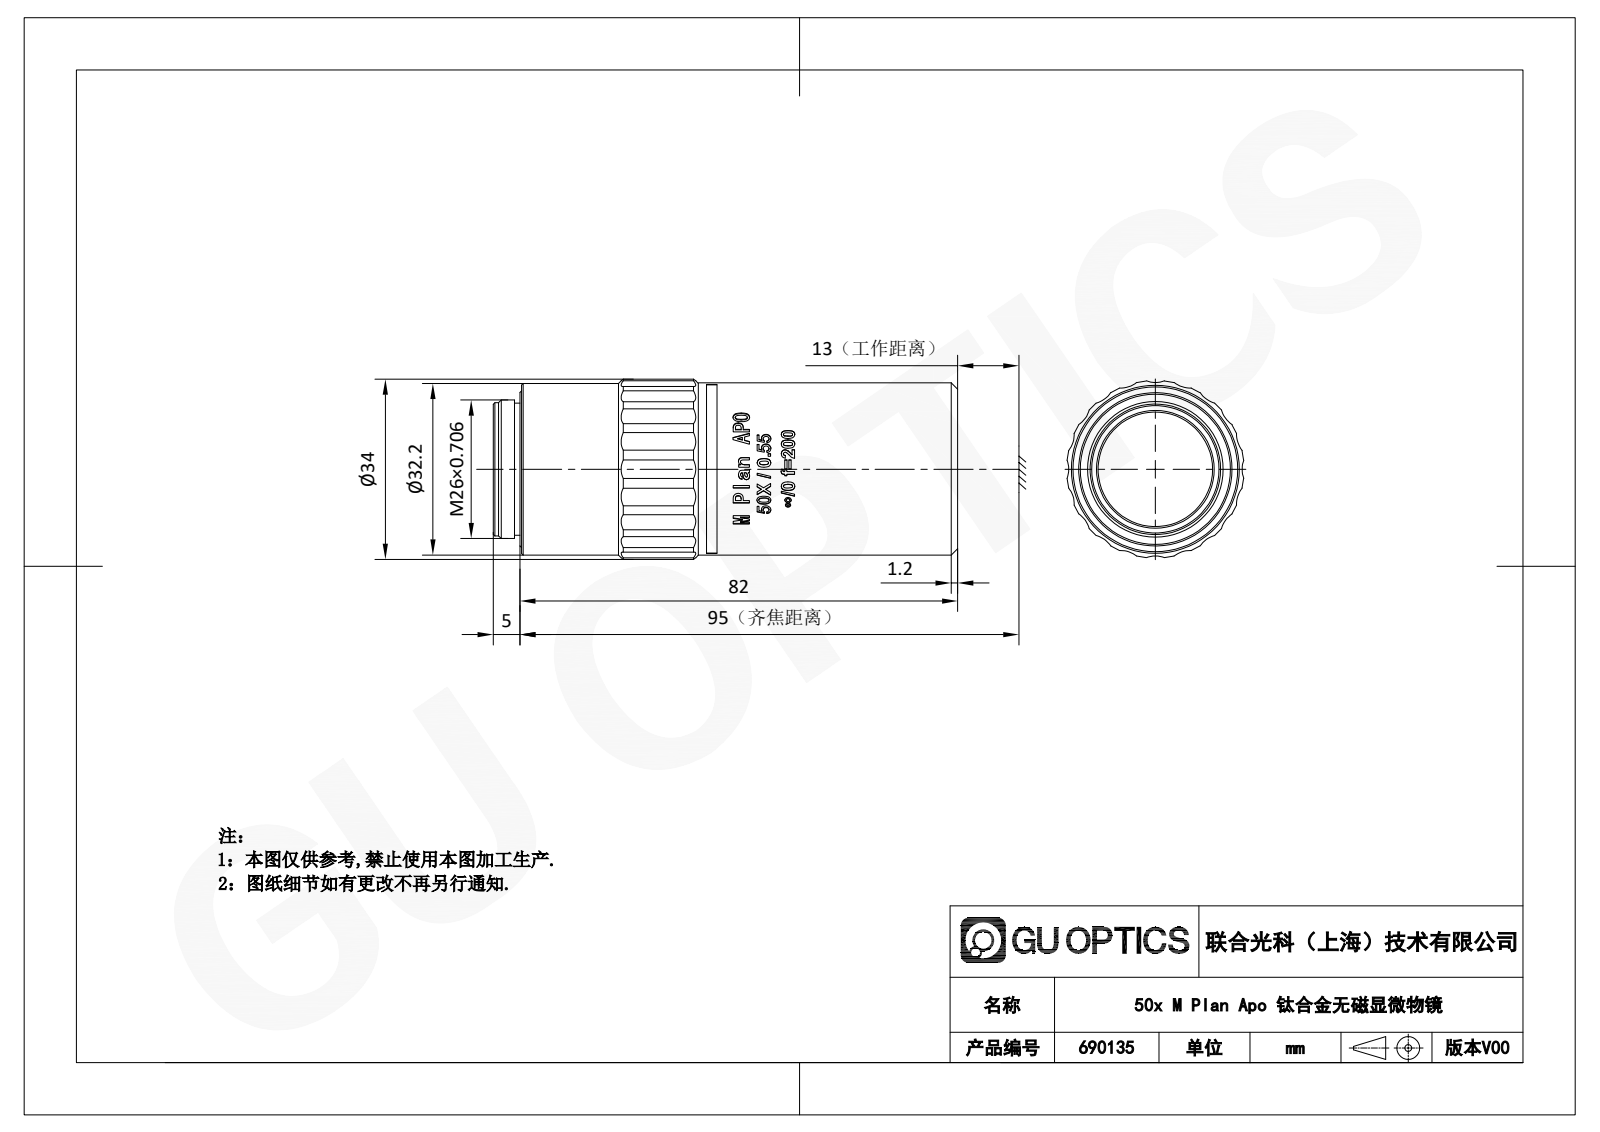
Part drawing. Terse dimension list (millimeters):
name: 690135
written by: SolidWorks 2020 (CONFIG_CONTROL_DESIGN)
unit: mm
bodies: 1 solid, 360 faces (103 planar, 86 cylindrical, 171 other)
size: 87 × 33.82 × 33.82
volume: 68 266 mm³; area: 10 829 mm²
holes: 1× ⌀22
bosses: 1× ⌀32.2, 1× ⌀32, 1× ⌀26, 1× ⌀25, 1× ⌀24.8
rounds: 20× R5, 1× R15.9, 1× R17
face distances: 83.3, 1.3, 82, 1.6, 81.7, 3.7, 5, 5.3, 87, 4
